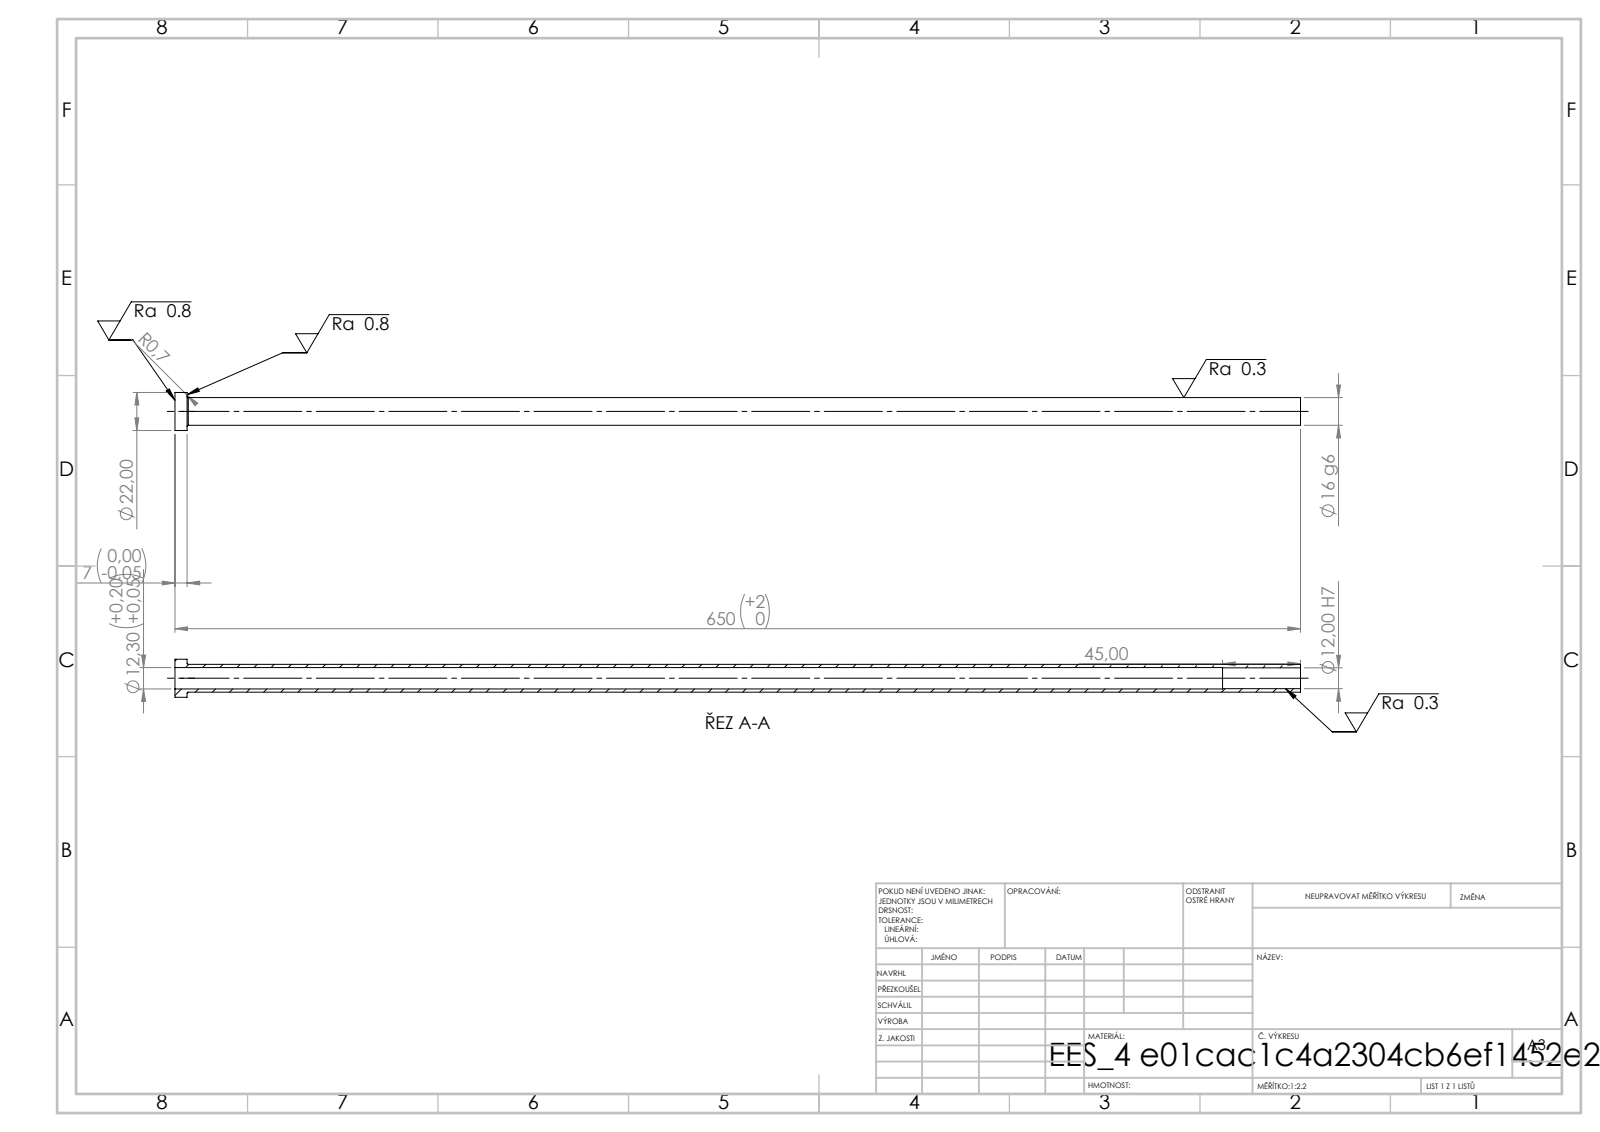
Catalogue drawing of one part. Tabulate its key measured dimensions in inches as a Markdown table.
| quantity | value |
| --- | --- |
| STEP written by | SolidWorks 2019 (CONFIG_CONTROL_DESIGN) |
| units | inches |
| bodies | 1 solid, 14 faces (4 planar, 8 cylindrical, 2 other) |
| overall size | 25.591 × 0.866 × 0.866 |
| volume | 3.355 in³ |
| surface area | 90.52 in² |
| round holes (diameter × count) | 0.472 × 1, 0.484 × 1 |
| round bosses / shafts (diameter × count) | 0.866 × 1, 0.63 × 1 |
| main face-to-face distances | 0.276, 25.591, 25.315, 23.819, 23.543, 1.772 |
